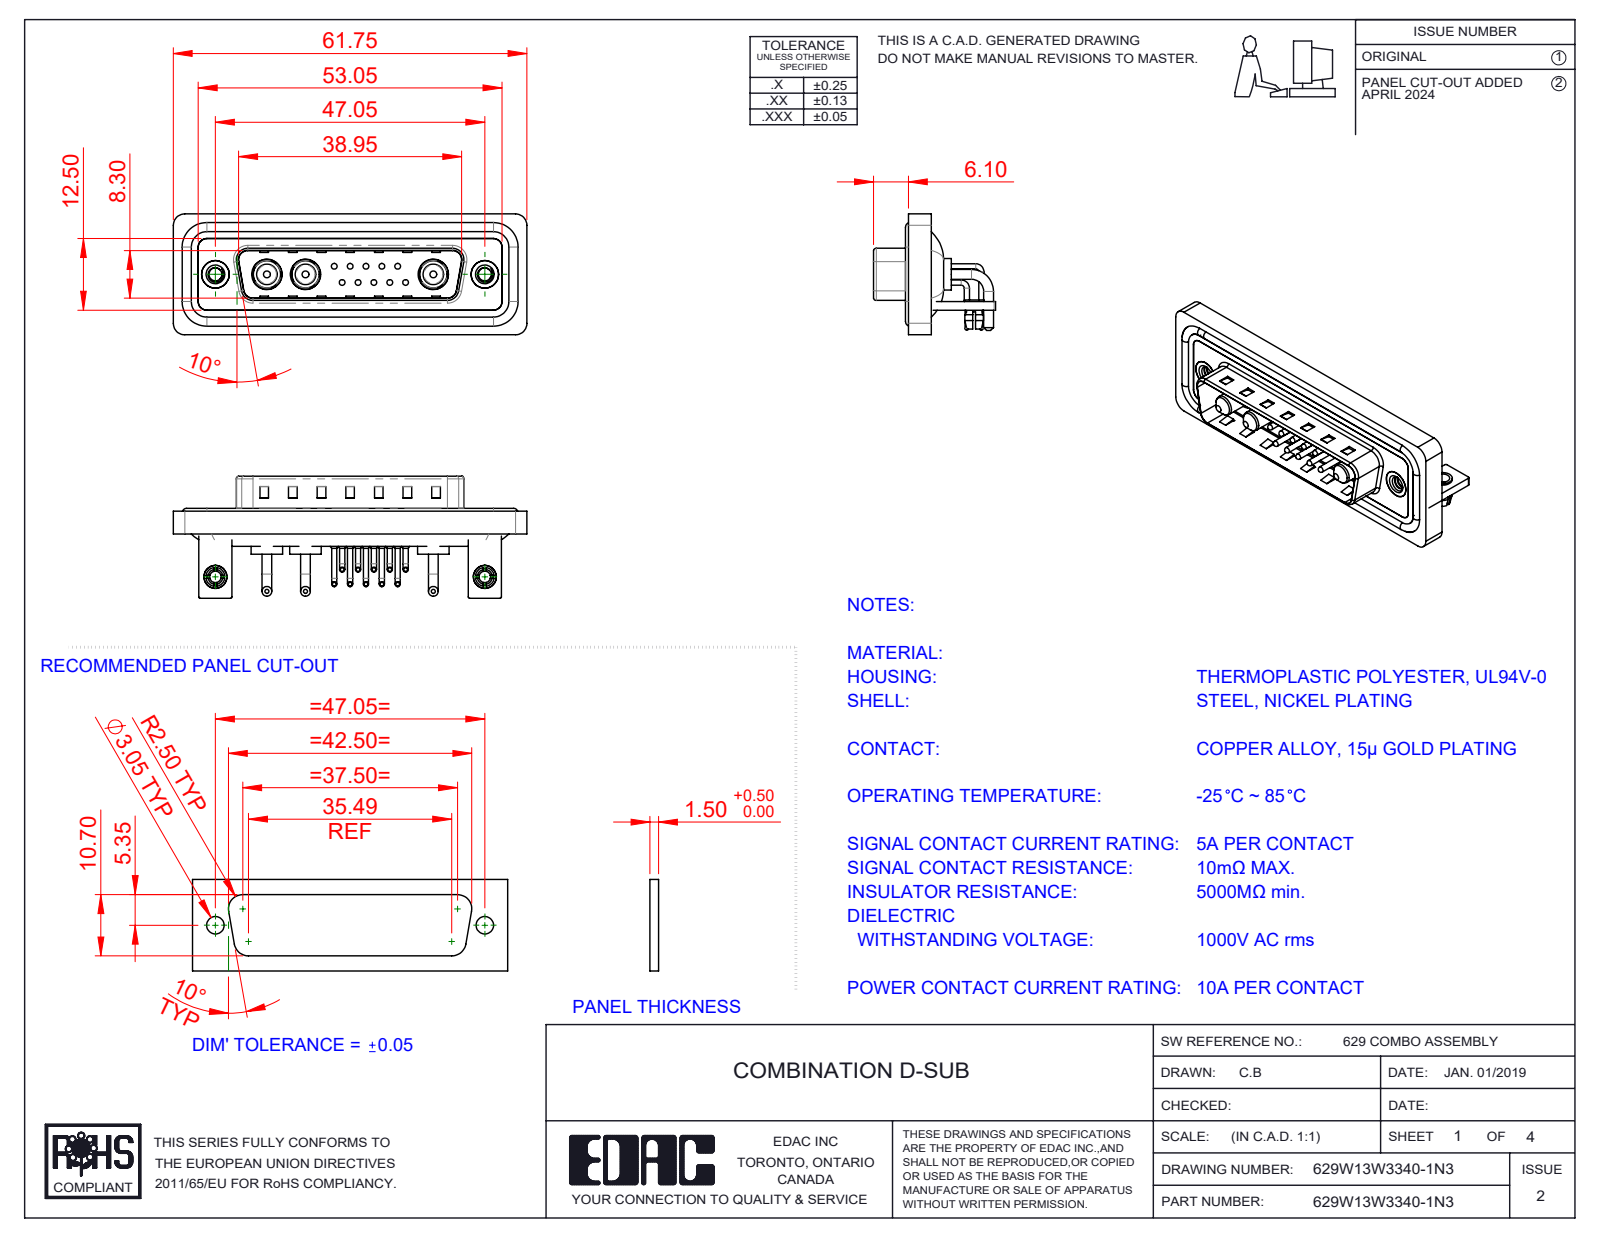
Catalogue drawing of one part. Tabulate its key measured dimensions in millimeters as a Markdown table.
| quantity | value |
| --- | --- |
| part name | 629Combo Waterproof Housing_25 Contacts; 629Combo Shell Rear_25 Contacts; 629Combo Threaded Rivet_3; 629Combo Contact Row 1 (+7 more) |
| STEP written by | SolidWorks 2023 (CONFIG_CONTROL_DESIGN) |
| units | millimeters |
| bodies | 27 solids, 1844 faces (947 planar, 661 cylindrical, 236 other) |
| overall size | 61.75 × 21.3 × 21.1 |
| volume | 7 750 mm³ |
| surface area | 13 141 mm² |
| round holes (diameter × count) | 2 × 12, 0.75 × 10, 1.6 × 10, 4.85 × 3, 5.3 × 3, 2.26 × 2, 2.5 × 2, 3.2 × 2, 4 × 2, 4.8 × 2, 5 × 2 |
| round bosses / shafts (diameter × count) | 0.9 × 20, 1.5 × 10, 1 × 10, 0.65 × 10, 1.7 × 6, 1.6 × 4, 5.5 × 3, 5.2 × 3 |
| partial cylindrical surfaces (radius × count) | 2 × 19, 1.5 × 18, 0.25 × 16, 1.01 × 10, 0.5 × 9, 1.6 × 8, 0.6 × 4, 0.65 × 4 |
| main face-to-face distances | 0.4, 1.5, 0.8, 2.9, 2.1, 1.1, 4.1, 1.6, 3.7, 4.5 |
| hole center spacings | 3.16, 2.77, 5.04, 5.54, 7.49, 5.03, 8.31, 10.11 |
